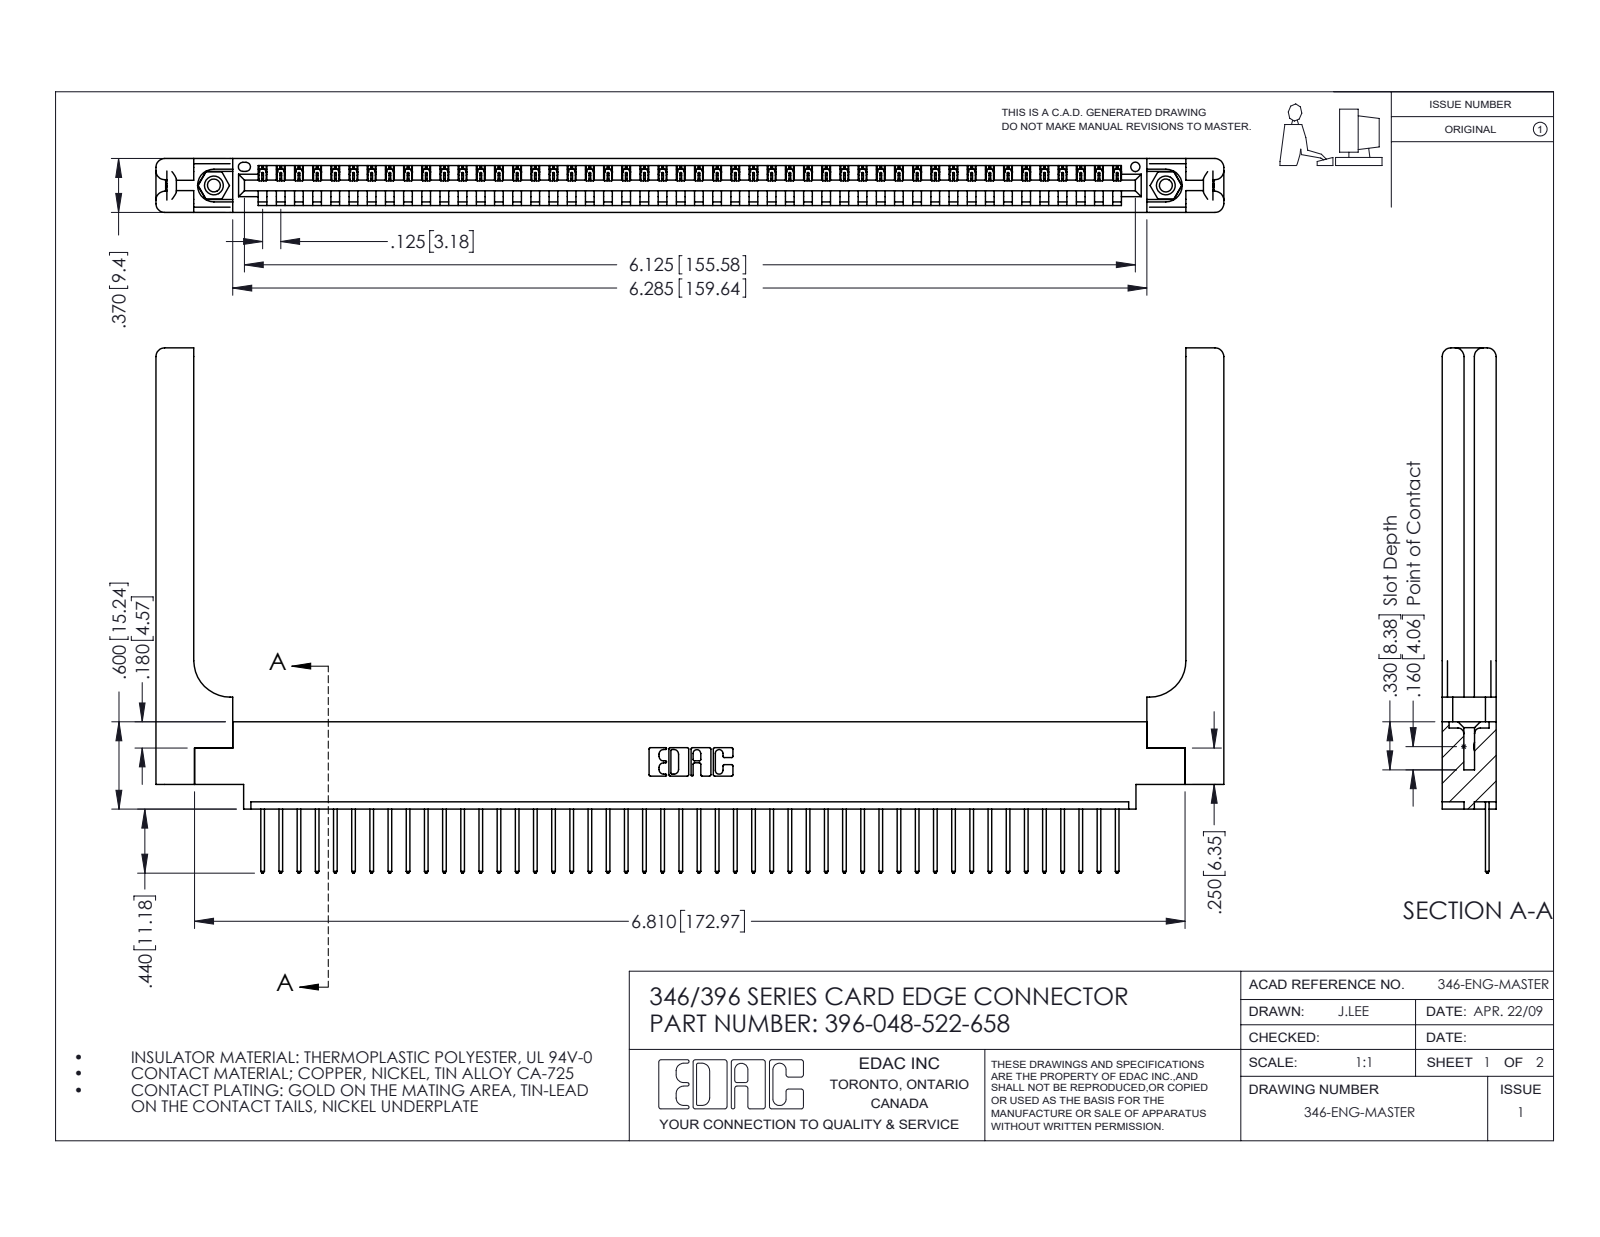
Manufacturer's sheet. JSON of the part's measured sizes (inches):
{"part_name": "345-292-001_345-293-122; 346 Part_0.170 Offset - 0.156 Dia-TH; 396-048-522-658; 346-220-058_345-220-058 (+1 more)", "step_written_by": "SolidWorks 2016 (CONFIG_CONTROL_DESIGN)", "units": "inches", "bodies": {"solids": 53, "faces": 3166, "planar": 2148, "cylindrical": 958, "other": 60}, "overall_size": [7.341, 3.61, 0.37], "volume_in3": 1.541, "surface_area_in2": 43.01, "round_holes": [[0.089, 2], [0.125, 2], [0.156, 2], [0.064, 1]], "round_bosses_or_shafts": [[0.155, 2]], "partial_cylinders_radius": [[0.006, 96], [0.01, 96], [0.01, 22], [0.06, 16], [0.007, 6], [0.031, 6], [0.026, 3], [0.03, 2]], "face_to_face_distances": [0.37, 0.048, 0.322, 0.072, 0.148, 0.15, 0.25, 0.298, 0.025, 0.222], "hole_center_spacings": [0.246, 6.336, 6.545]}
